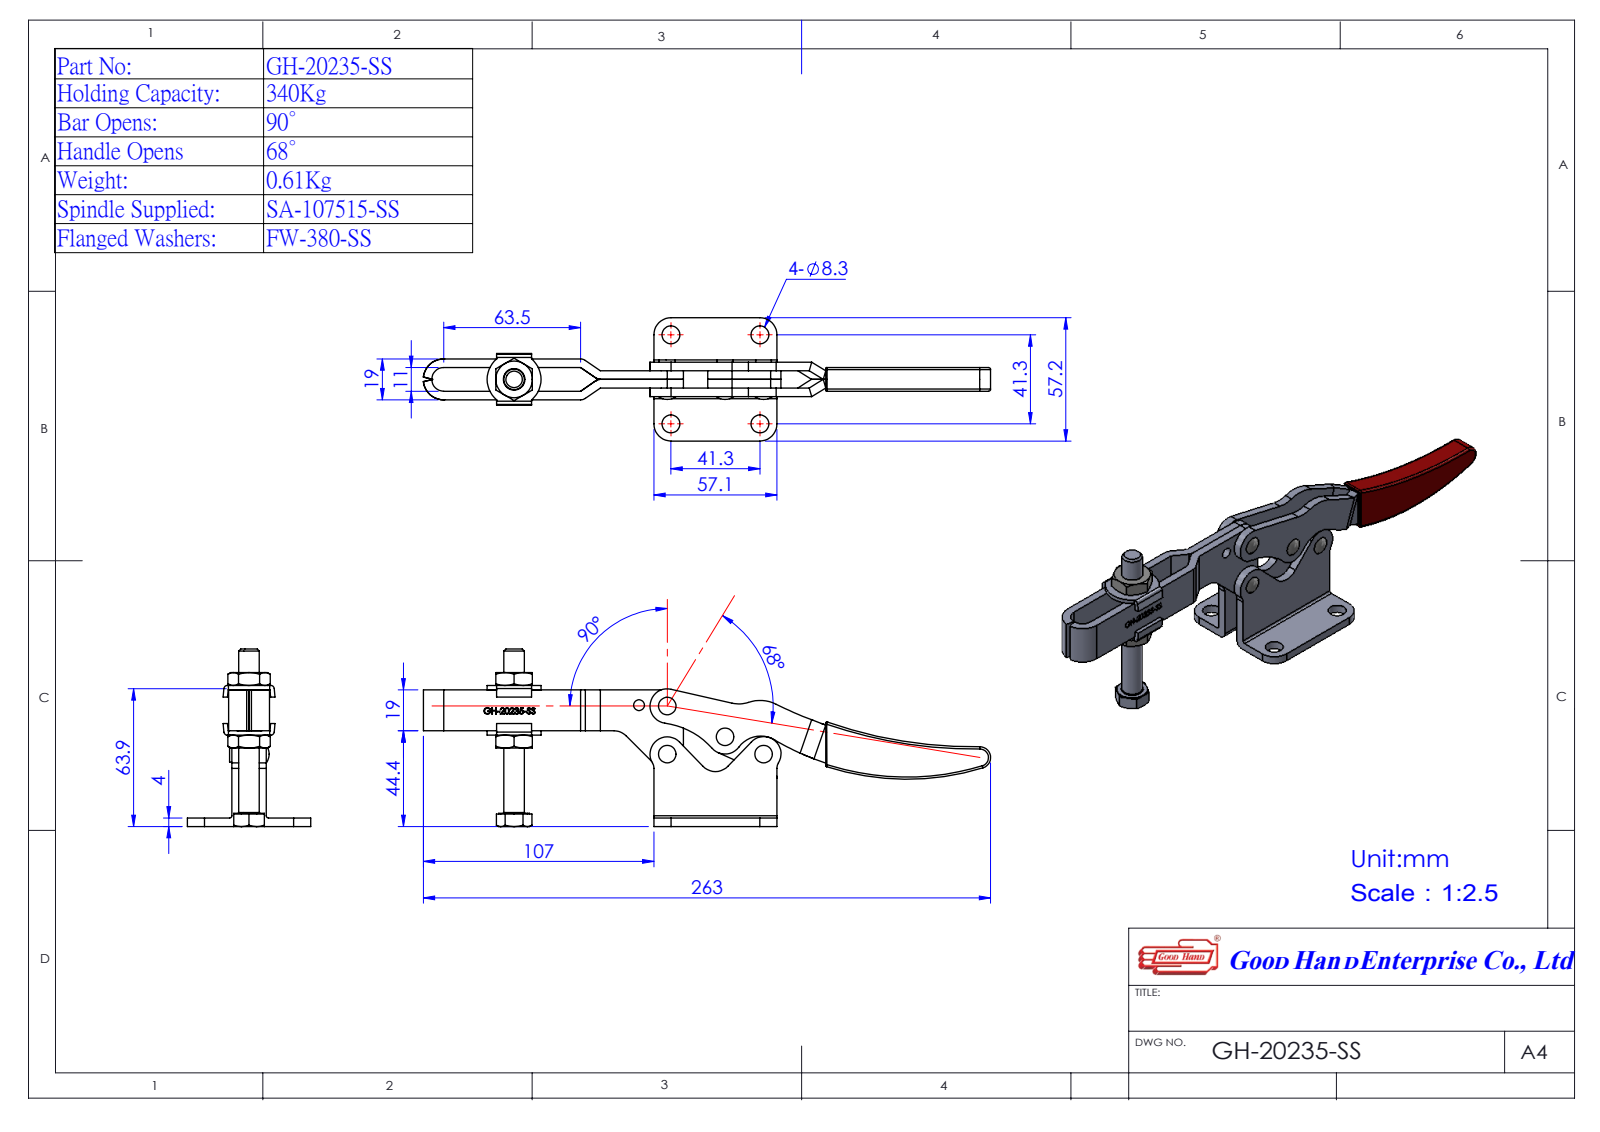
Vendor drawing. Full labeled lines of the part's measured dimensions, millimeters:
Part name (STEP PRODUCT): GH-20235-SS(簡化)-1; Group6^GH-20235-SS(簡化)-1; 12023508-1^GH-20235-SS(簡化)-1; Group3^GH-20235-SS(簡化)-1 (+2 more)
STEP written by: SolidWorks 2016 (AUTOMOTIVE_DESIGN)
Units: millimetres
Bodies: 5 solids, 290 faces (118 planar, 120 cylindrical, 52 other)
Overall size (bounding box): 264.56 × 82.37 × 57.2
Volume: 87 442 mm³ · Surface area: 47 717 mm²
Round holes (diameter × count): ⌀5 ×4, ⌀8.3 ×4
Round bosses / shafts (diameter × count): ⌀7.35 ×4, ⌀5 ×3, ⌀6.35 ×2, ⌀14.27 ×1, ⌀9.52 ×1
Partial cylindrical surfaces — rounded edges, fillets, slot ends (radius × count): R8 ×6, R1.5 ×4, R5 ×4, R7.95 ×4, R7.5 ×2, R2 ×1, R2.8 ×1, R5.5 ×1
Main face-to-face distances: 4, 8, 13.5, 1.5, 9.5, 5.5, 12, 2.5, 16, 17.5
Hole centre spacings: 41.3, 58.41, 19.6, 22.3, 28, 30.38, 44.7, 49.95
